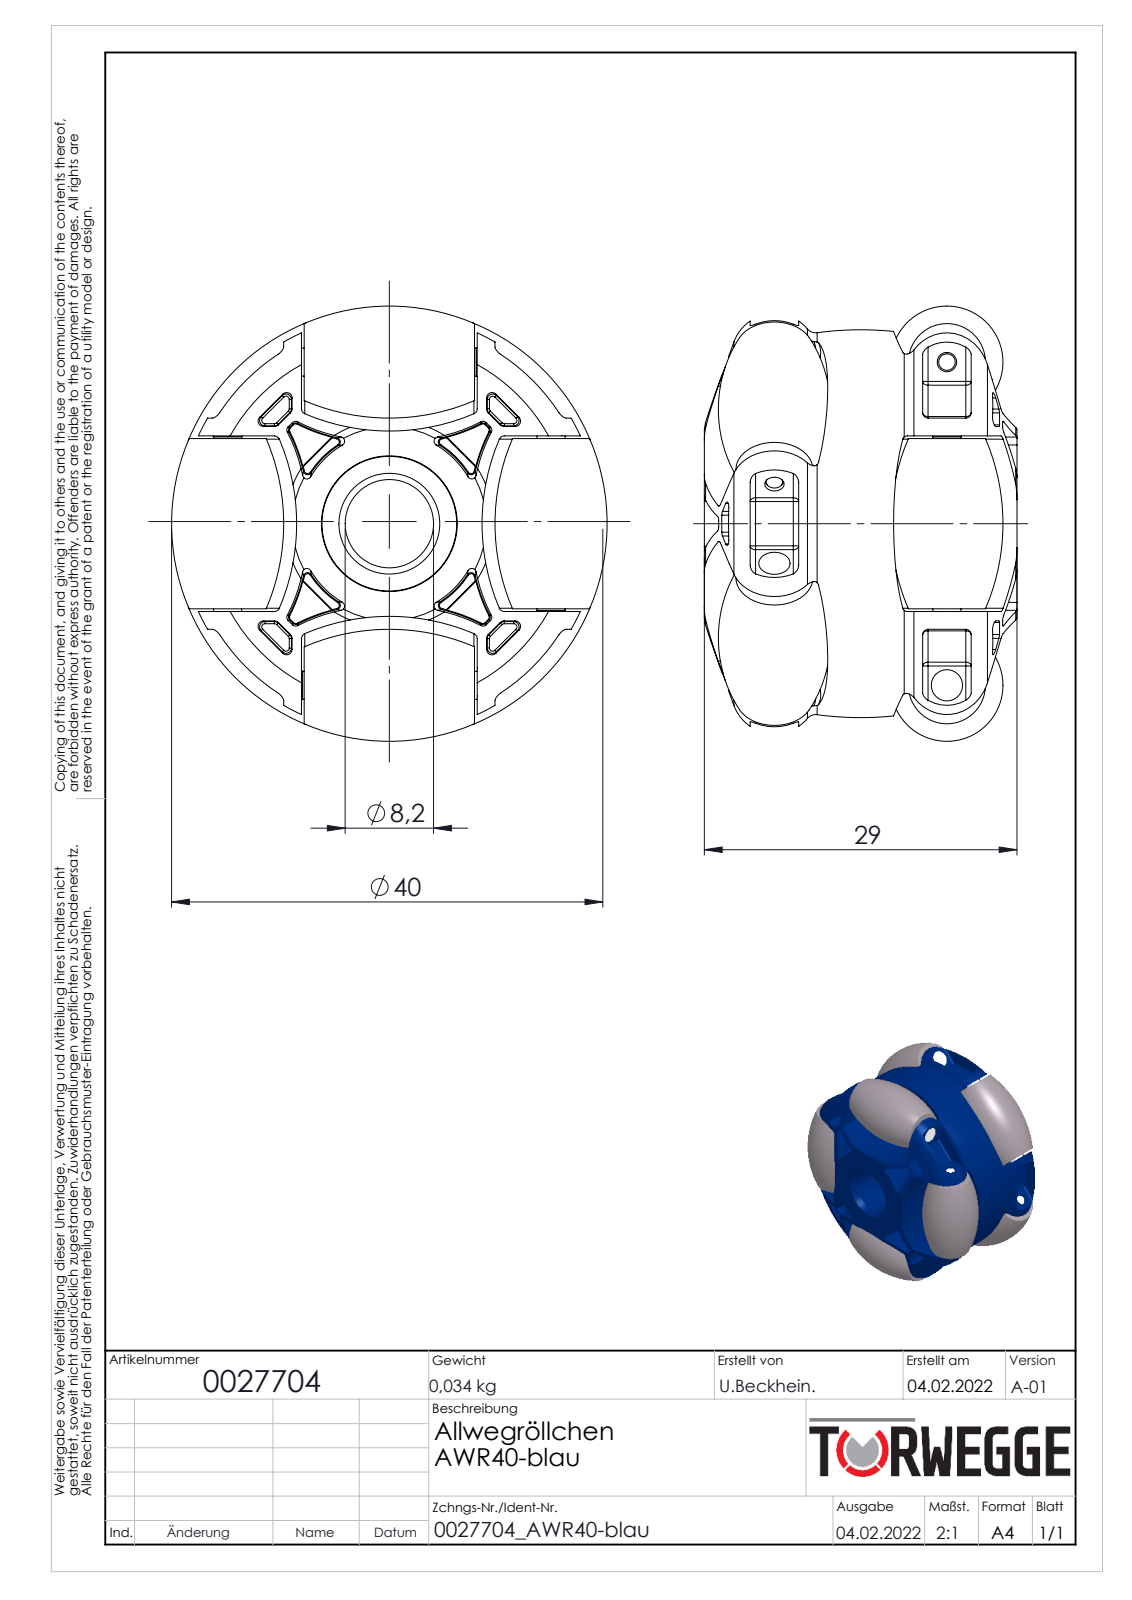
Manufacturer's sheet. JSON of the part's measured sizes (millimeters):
{"part_name": "0027704", "step_written_by": "SolidWorks 2020 (AUTOMOTIVE_DESIGN)", "units": "millimeters", "bodies": {"solids": 19, "faces": 1001, "planar": 160, "cylindrical": 370, "other": 471}, "overall_size": [40.4, 40.4, 29], "volume_mm3": 21278, "surface_area_mm2": 18690, "round_holes": [[1.8, 8], [2.7, 8], [2.9, 8], [3.1, 8], [8.2, 1], [10.8, 1], [12.35, 1], [12.6, 1]], "round_bosses_or_shafts": [[3, 8], [2.6, 8], [2, 8], [12.5, 1]], "partial_cylinders_radius": [[0.5, 104], [0.2, 28], [0.1, 16], [5.5, 8], [20, 8]], "face_to_face_distances": [16.05, 16.3, 15.8, 6.37, 22.88, 29.25, 29, 17.7, 1.65, 1.9], "hole_center_spacings": [30, 30.01]}
